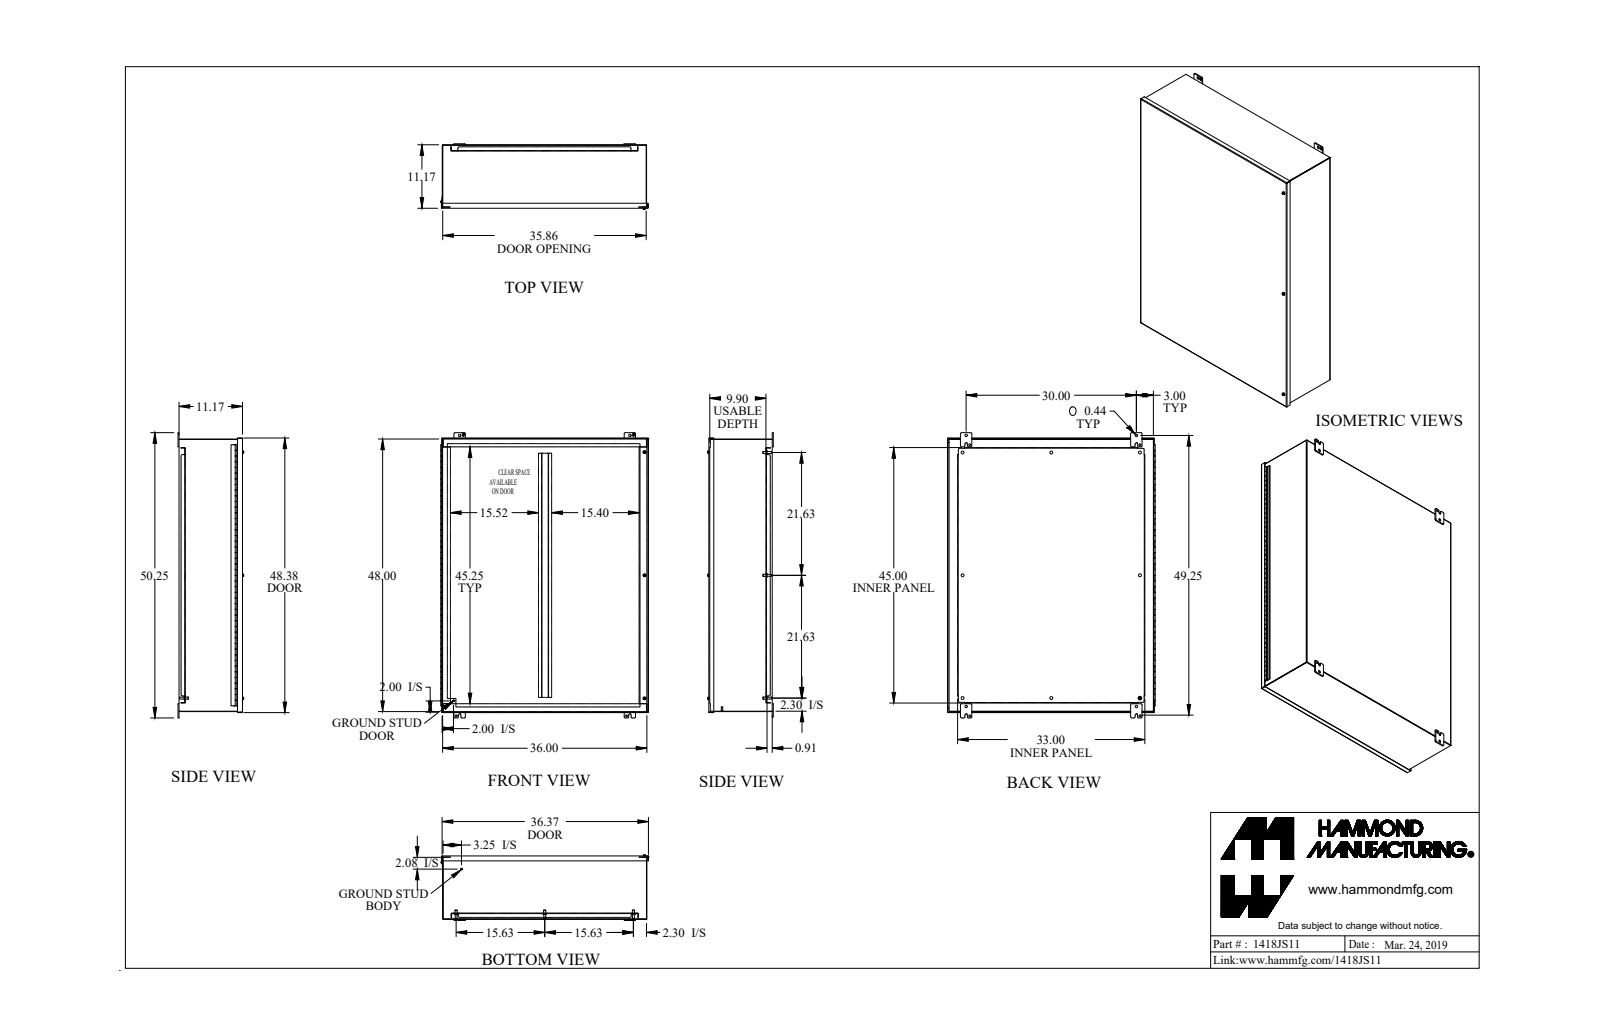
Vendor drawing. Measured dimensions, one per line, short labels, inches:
name: 1418JS11_Default
written by: SolidWorks 2018 (CONFIG_CONTROL_DESIGN)
unit: in
bodies: 50 solids, 1421 faces (820 planar, 523 cylindrical, 78 other)
size: 50.25 × 36.604 × 11.571
volume: 641.5 in³; area: 16 208 in²
holes: 8× ⌀0.5, 7× ⌀0.313, 4× ⌀0.307, 4× ⌀0.437, 4× ⌀0.445, 3× ⌀0.26, 3× ⌀0.266, 3× ⌀0.28, 3× ⌀0.29, 3× ⌀0.397, 1× ⌀0.187, 1× ⌀3.5
bosses: 8× ⌀0.65, 8× ⌀0.375, 8× ⌀0.33, 4× ⌀1, 3× ⌀0.51, 3× ⌀0.5, 3× ⌀0.39, 3× ⌀0.244
rounds: 35× R0.188, 28× R0.25, 16× R0.116, 10× R0.036, 10× R0.108, 8× R0.218, 7× R0.125, 6× R0.133
face distances: 0.072, 11.1, 11.028, 11.172, 0.095, 1.104, 1.032, 9.996, 10.068, 1.009
hole spacings: 38.003, 45.986, 1.735, 21.687, 21.688, 30, 43.25, 47.75
